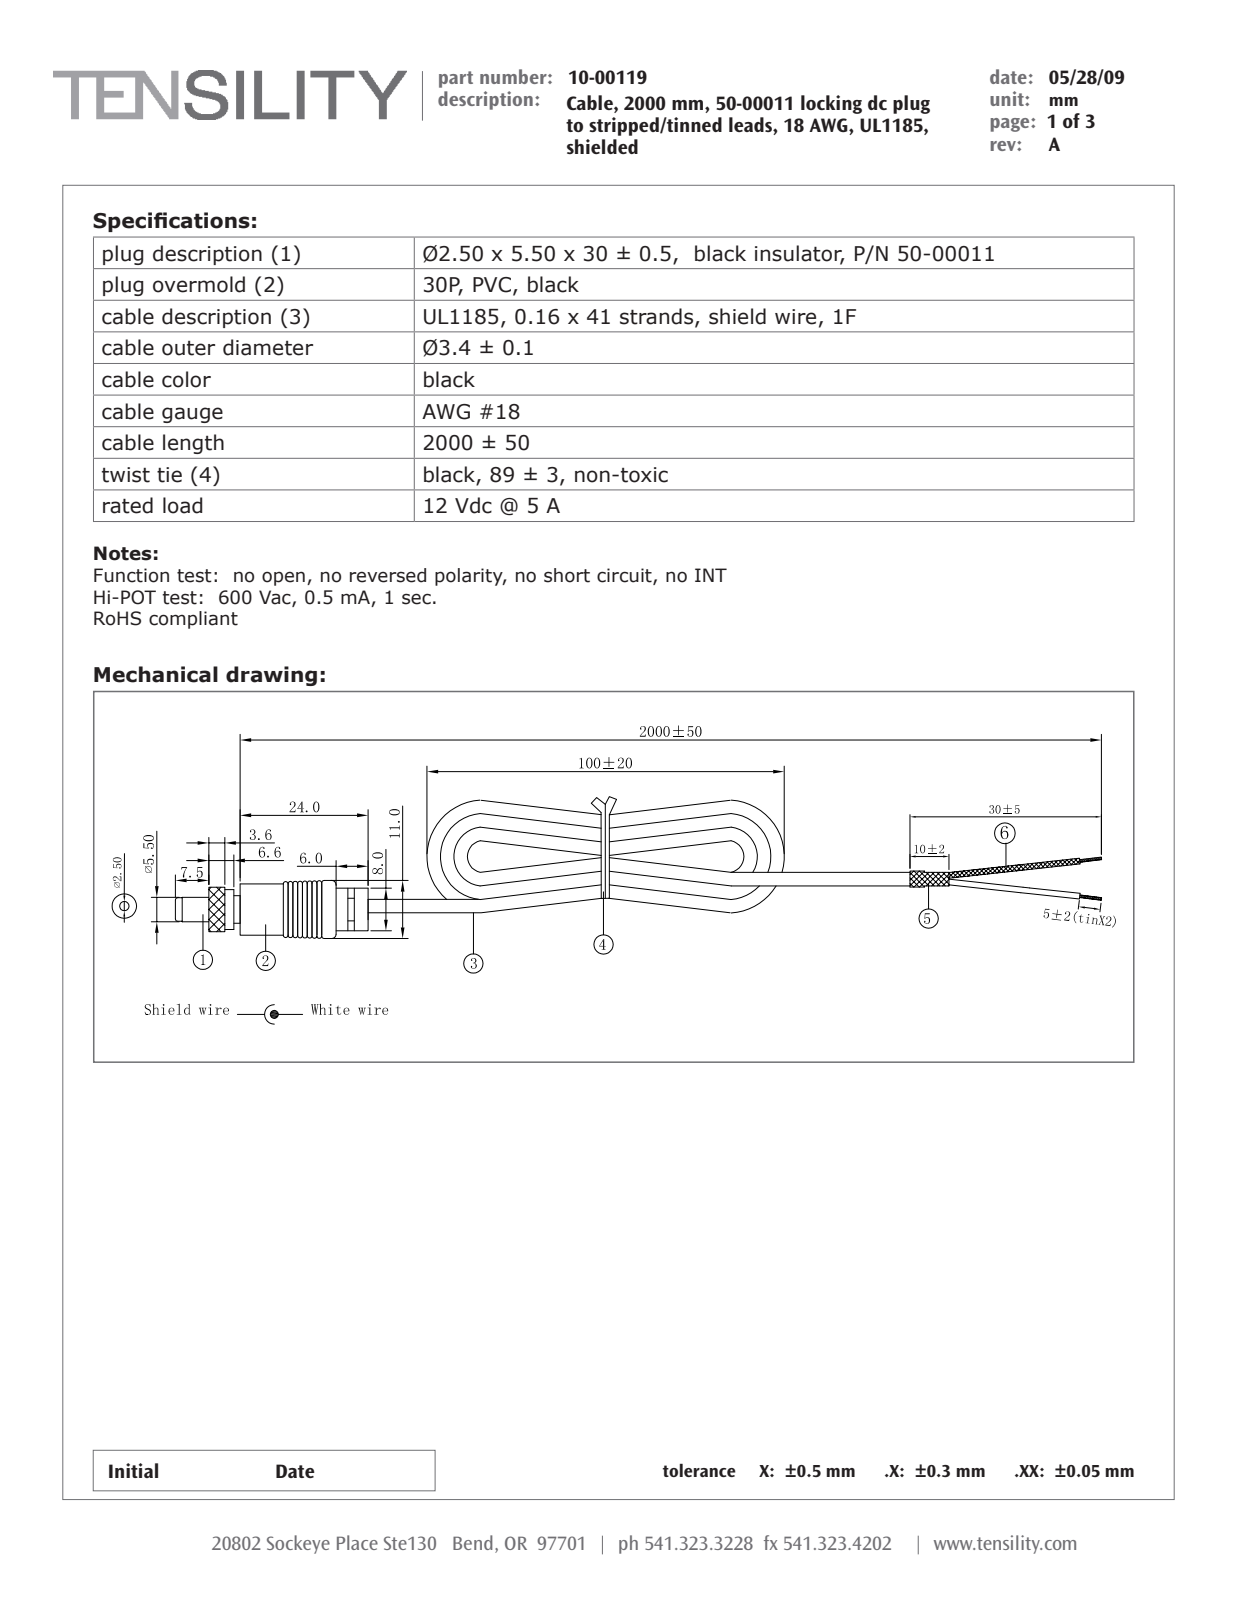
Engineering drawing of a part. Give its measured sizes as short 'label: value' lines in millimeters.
name: 50-00011; 30-00004_wst; 50-00011 shell 2; 50-00011 locking ring (+6 more)
written by: SolidWorks 2015 (CONFIG_CONTROL_DESIGN)
unit: mm
bodies: 93 solids, 1650 faces (519 planar, 405 cylindrical, 726 other)
size: 210.8 × 11 × 11
volume: 3 298 mm³; area: 7 355 mm²
holes: 1× ⌀1.6, 1× ⌀2.16, 1× ⌀2.4, 1× ⌀2.5, 1× ⌀3, 1× ⌀3.25, 1× ⌀4.25, 1× ⌀5.04, 1× ⌀5.44, 1× ⌀5.5, 1× ⌀5.65, 1× ⌀6.4
bosses: 1× ⌀11, 1× ⌀10, 1× ⌀8, 1× ⌀7, 1× ⌀6.2, 1× ⌀6, 1× ⌀5.48, 1× ⌀5.3
rounds: 8× R0.2, 4× R0.55, 1× R3.92
face distances: 1.5, 24, 13.4, 2.6, 21.4, 23.2, 19.9, 4.1, 3.4, 32.4
